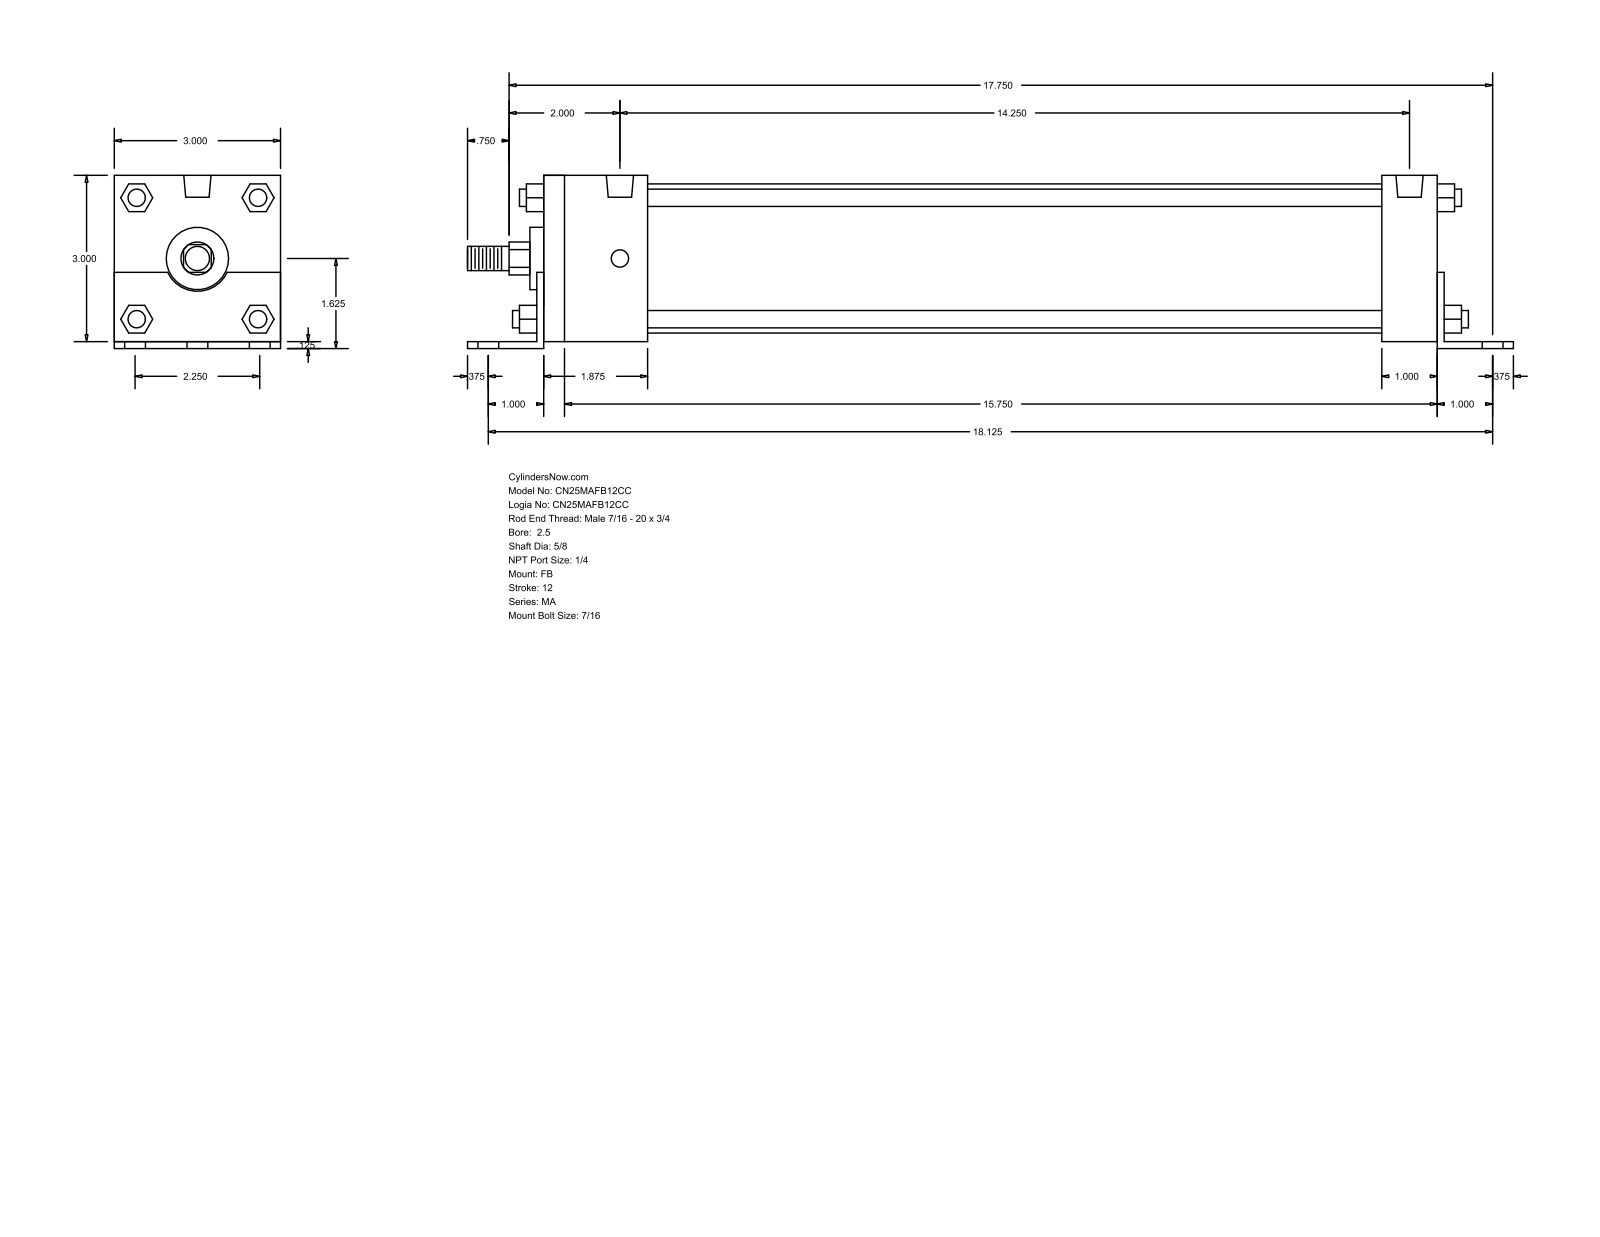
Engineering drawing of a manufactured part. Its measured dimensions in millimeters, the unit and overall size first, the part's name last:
Units: millimetres
Overall size (bounding box): 479.43 × 79.38 × 76.2
Round holes (diameter × count): ⌀11.11 ×6, ⌀7.94 ×4, ⌀12.49 ×2
Round bosses / shafts (diameter × count): ⌀7.94 ×4, ⌀68.33 ×1, ⌀28.57 ×1, ⌀15.88 ×1, ⌀11.11 ×1
Partial cylindrical surfaces — rounded edges, fillets, slot ends (radius × count): R7.54 ×1, R15.05 ×1
Main face-to-face distances: 76.2, 3.17, 79.37, 409.57, 415.92, 3.18, 412.74, 47.62, 25.4, 412.75
Hole centre spacings: 28.57, 461.27, 460.38, 47.62, 57.14, 66.75, 361.95, 401.07
Bodies: 0 solids, 140 faces (105 planar, 35 cylindrical, 0 other)
Part name (STEP PRODUCT): MA_FB__0250_0.625
STEP written by: GSSL Pune (CONFIG_CONTROL_DESIGN)
